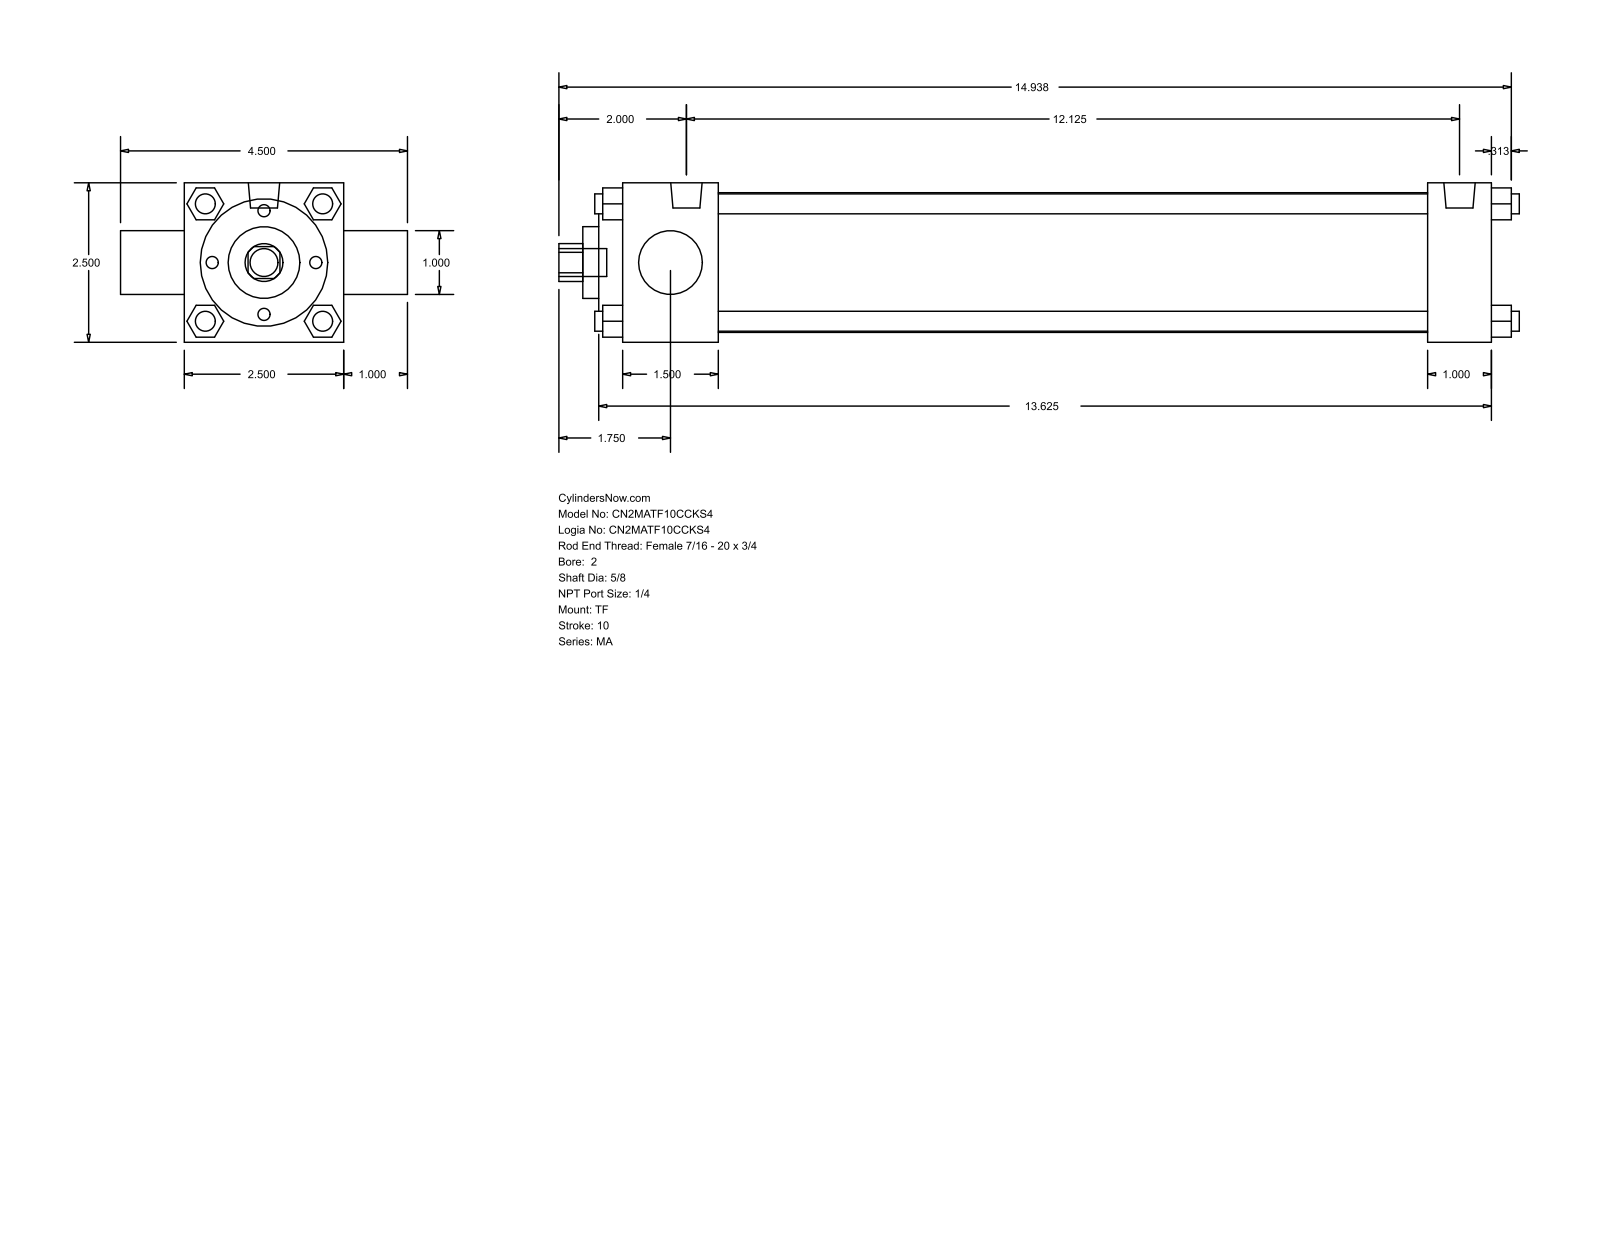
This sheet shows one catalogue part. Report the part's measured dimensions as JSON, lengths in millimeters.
{"part_name": "MA_TF__0200_0.625", "step_written_by": "GSSL Pune (CONFIG_CONTROL_DESIGN)", "units": "millimeters", "bodies": {"solids": 0, "faces": 122, "planar": 93, "cylindrical": 29, "other": 0}, "overall_size": [382.59, 114.3, 63.5], "round_holes": [[15.88, 1], [25.4, 1], [28.57, 1], [50.8, 1], [55.63, 1]], "round_bosses_or_shafts": [[7.94, 7], [12.49, 2], [11.11, 1]], "partial_cylinders_radius": [[7.54, 1]], "face_to_face_distances": [63.5, 38.1, 12.7, 9.52, 346.08, 320.67, 282.57, 307.98, 25.41, 47.62]}
